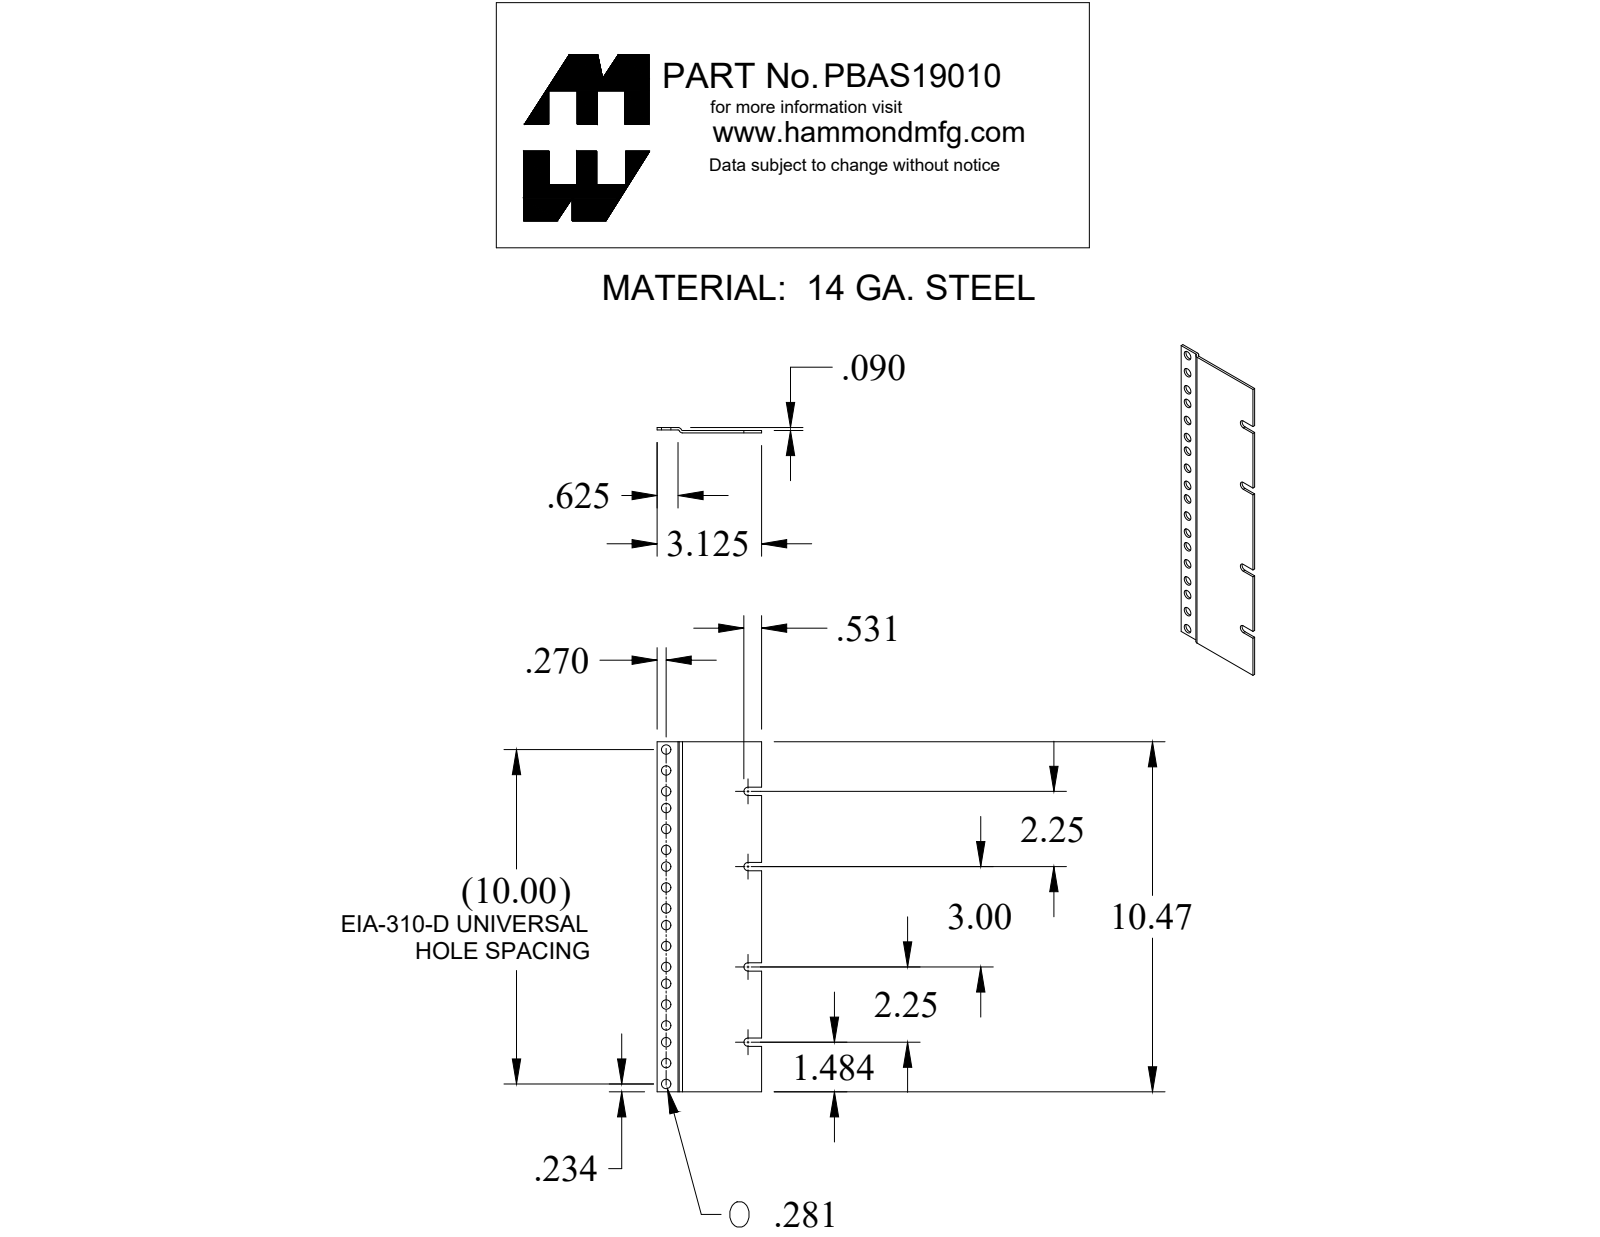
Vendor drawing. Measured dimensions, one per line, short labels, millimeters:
name: PBAS19010BK2
written by: SolidWorks 2019 (CONFIG_CONTROL_DESIGN)
unit: mm
bodies: 1 solid, 46 faces (20 planar, 26 cylindrical, 0 other)
size: 265.9 × 79.4 × 4.1
volume: 37 150 mm³; area: 42 810 mm²
holes: 18× ⌀7.1
rounds: 4× R3.2, 2× R0.9, 2× R2.7
face distances: 1.8, 4.1, 2.3, 2.3, 0.5, 1.8, 79.4, 265.9, 57.2, 6.4
hole spacings: 44.5, 88.9, 15.9, 15.9, 28.6, 31.8, 60.3, 73
